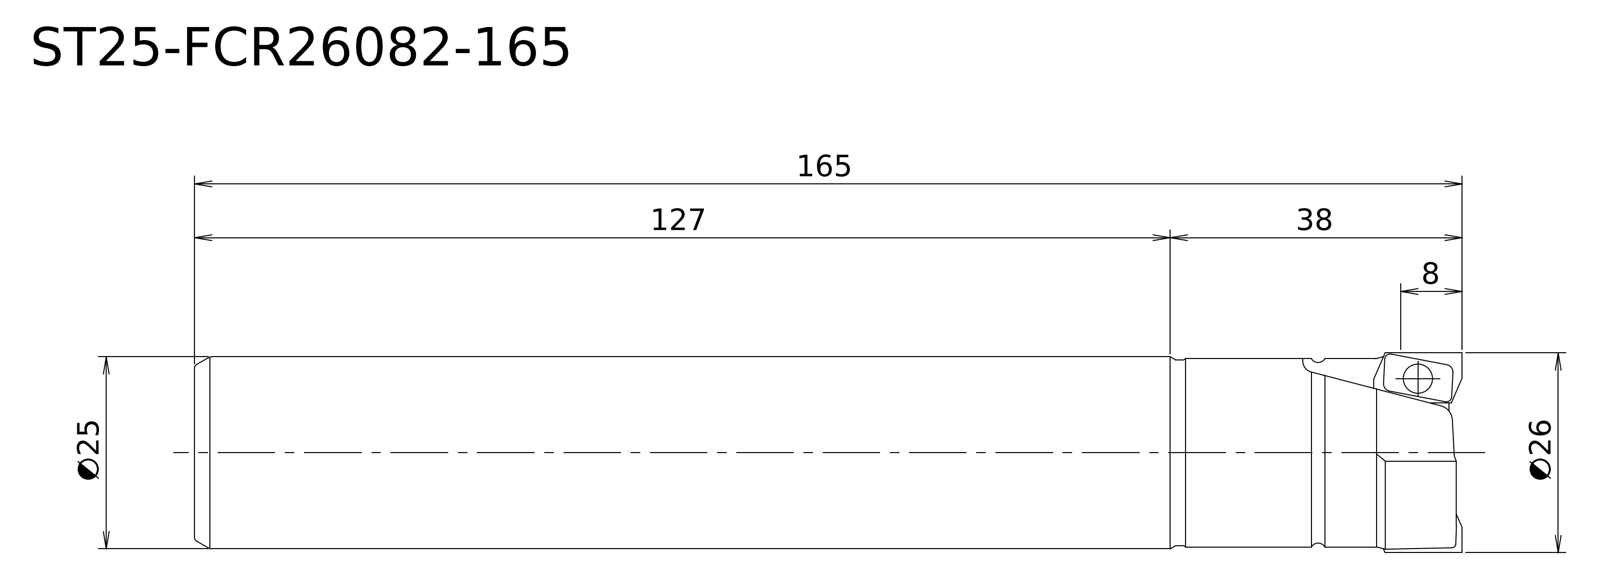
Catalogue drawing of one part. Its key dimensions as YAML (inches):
step_written_by: "Kubotek KeyCreator V8.5.1 (14335) (CONFIG_CONTROL_DESIGN)"
units: inches
bodies: {solids: 1, faces: 7, planar: 2, cylindrical: 3, other: 2}
overall_size: [6.496, 1.024, 1.024]
volume: 4.935
surface_area: 21.72
round_bosses_or_shafts:
  - {diameter: 1.024, count: 1}
  - {diameter: 0.984, count: 1}
  - {diameter: 0.965, count: 1}
face_to_face_distances: [6.496]
